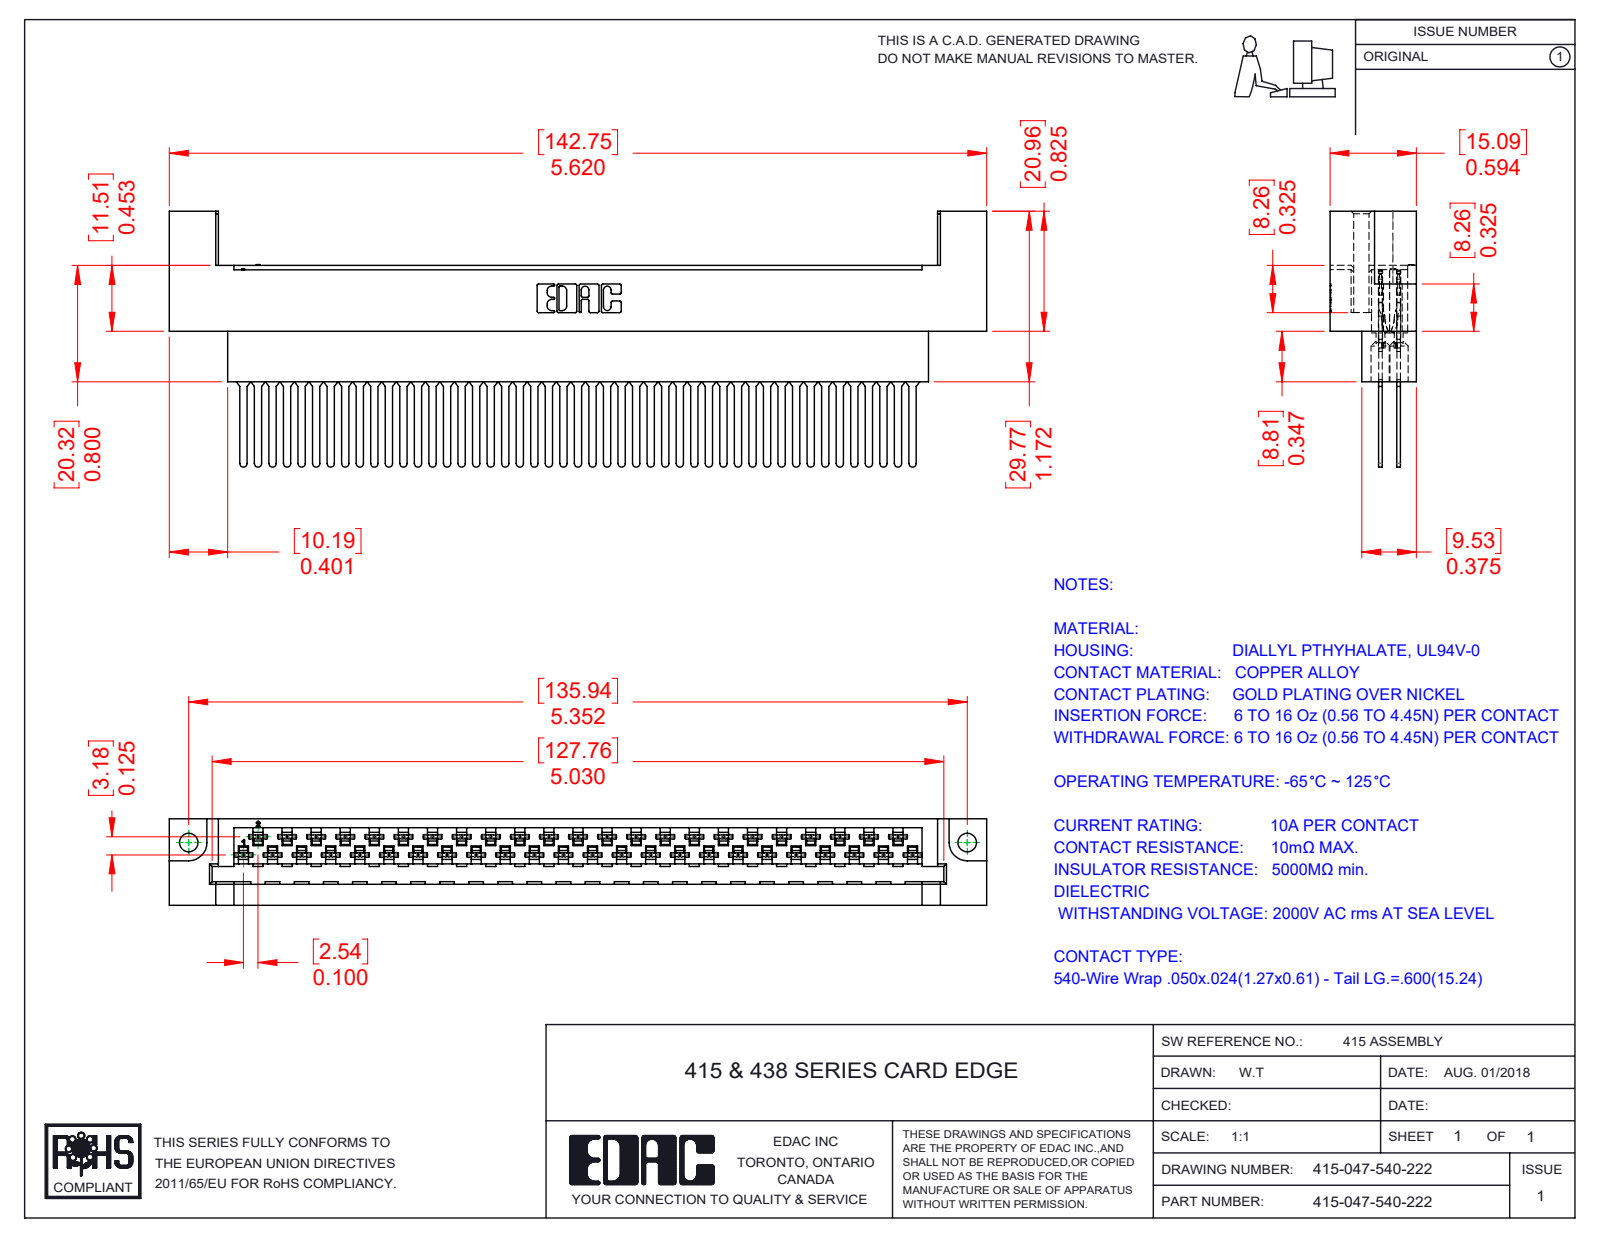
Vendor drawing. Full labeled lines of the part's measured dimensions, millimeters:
Part name (STEP PRODUCT): 516-290-001_540; 415-210-001_415-210-047-222; 415-047-540-222
STEP written by: SolidWorks 2016 (CONFIG_CONTROL_DESIGN)
Units: millimetres
Bodies: 48 solids, 4768 faces (3055 planar, 1268 cylindrical, 445 other)
Overall size (bounding box): 142.75 × 44.66 × 15.09
Volume: 27 420 mm³ · Surface area: 32 804 mm²
Round holes (diameter × count): ⌀1.27 ×47, ⌀3.3 ×47, ⌀3.25 ×2
Partial cylindrical surfaces — rounded edges, fillets, slot ends (radius × count): R0.3 ×188, R0.56 ×188, R0.18 ×94, R0.2 ×94, R0.41 ×94, R2.03 ×94, R0.64 ×47, R0.25 ×22
Main face-to-face distances: 3.18, 0.61, 15.09, 1.27, 1.88, 6.61, 8.48, 6, 9.09, 2.82
Hole centre spacings: 5.08, 10.16, 15.24, 20.32, 25.4, 30.48, 35.56, 2.54
